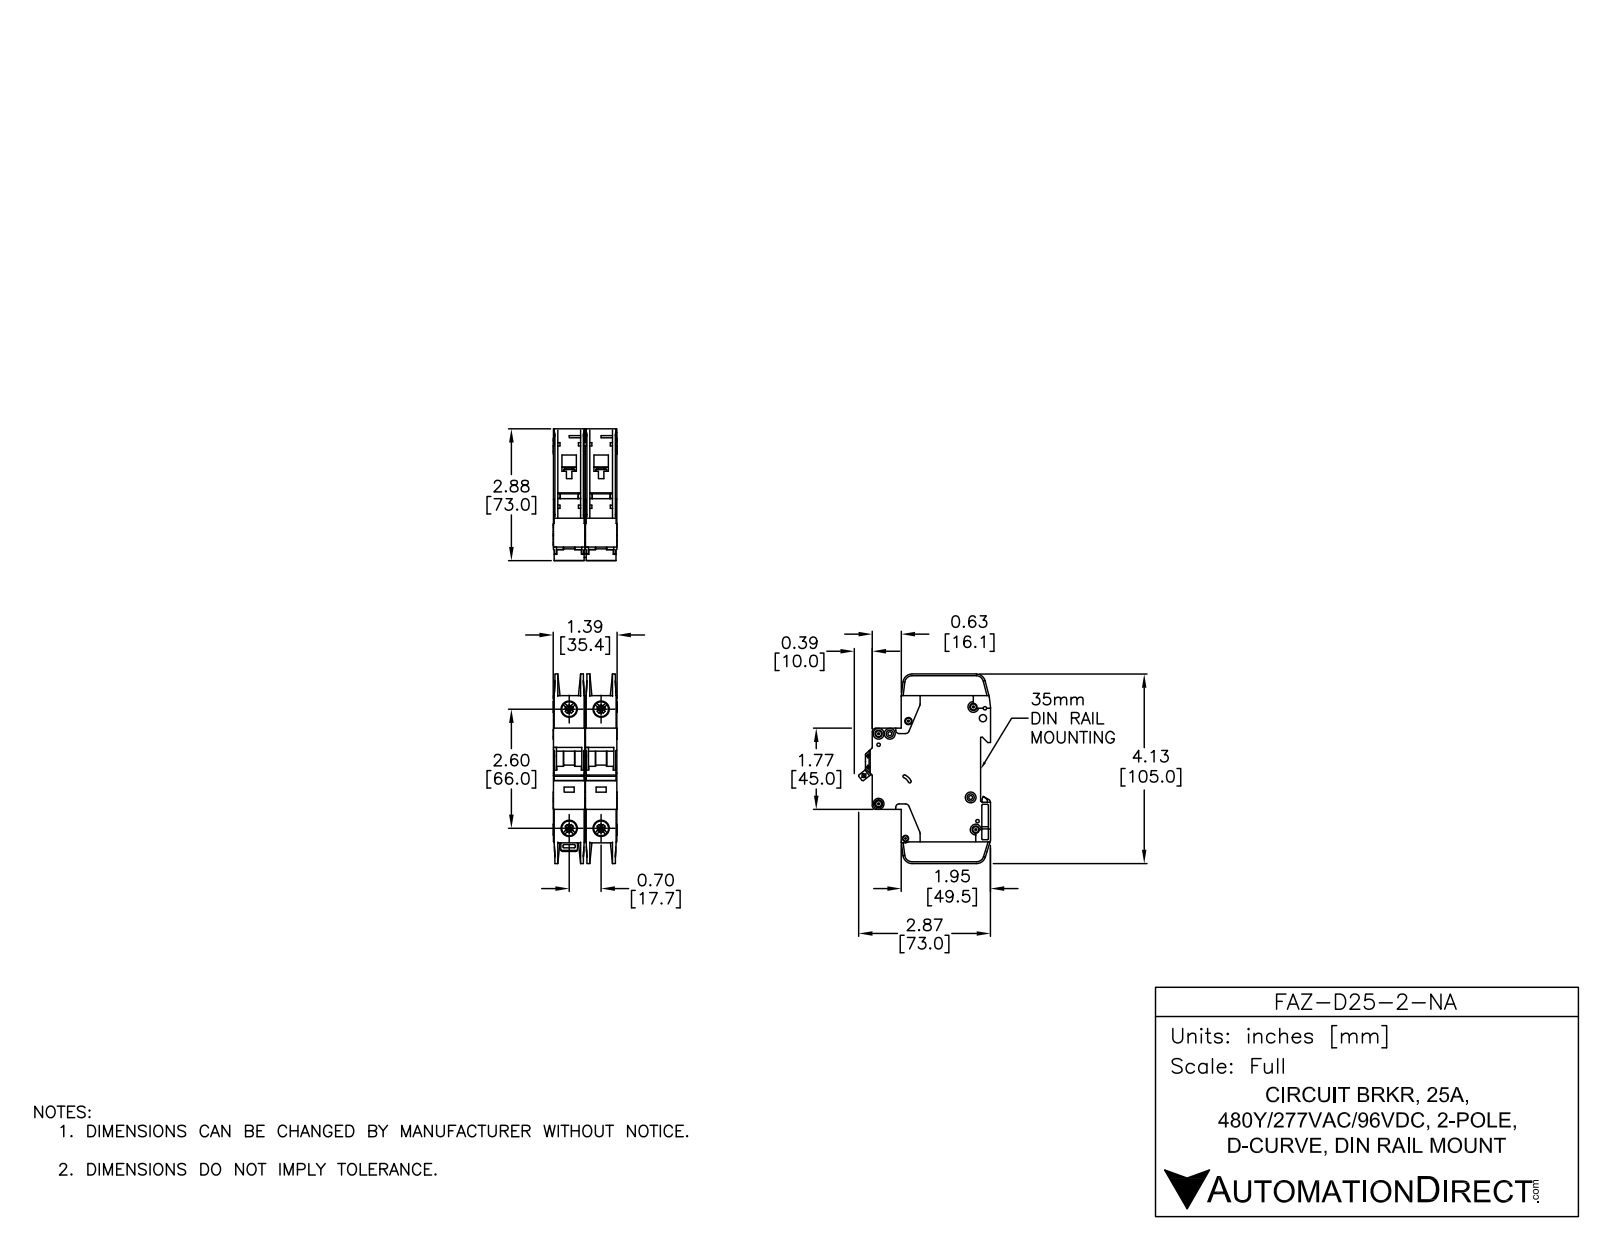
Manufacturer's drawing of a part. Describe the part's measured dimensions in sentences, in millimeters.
The part is named "FAZ-D25-2-NA". Its 3-D file was written by "SolidWorks 2014 (AUTOMOTIVE_DESIGN)". It is 6 solids with 1568 faces: 818 planar, 526 cylindrical and 224 other. Overall it measures 105 by 73.04 by 35.4 millimeters. Its volume is 155 390 cubic millimeters and its surface area 49 479 square millimeters. Round holes: 7 of diameter 3.6, 4 of diameter 7.15, 4 of diameter 8.2, 2 of diameter 1.09, 2 of diameter 1.5, 2 of diameter 4, 1 of diameter 1.9, 1 of diameter 2.15, 1 of diameter 2.2, 1 of diameter 2.55, 1 of diameter 3.3, 1 of diameter 3.4. Round bosses or shafts: 7 of diameter 6, 2 of diameter 2.5. Partial cylindrical surfaces (rounded edges, fillets, slot ends): 47 of radius 0.25, 24 of radius 0.5, 18 of radius 1, 12 of radius 2, 5 of radius 5, 4 of radius 1.8, 4 of radius 4, 2 of radius 0.2. The main face-to-face distances are 17.7, 17.5, 0.7, 15.05, 2.45, 1.75, 15.75, 13.3, 35.2, 17. The hole center spacings are 6.2, 17.7, 66, 68.33, 5.19, 6.1, 8.19, 8.56.
